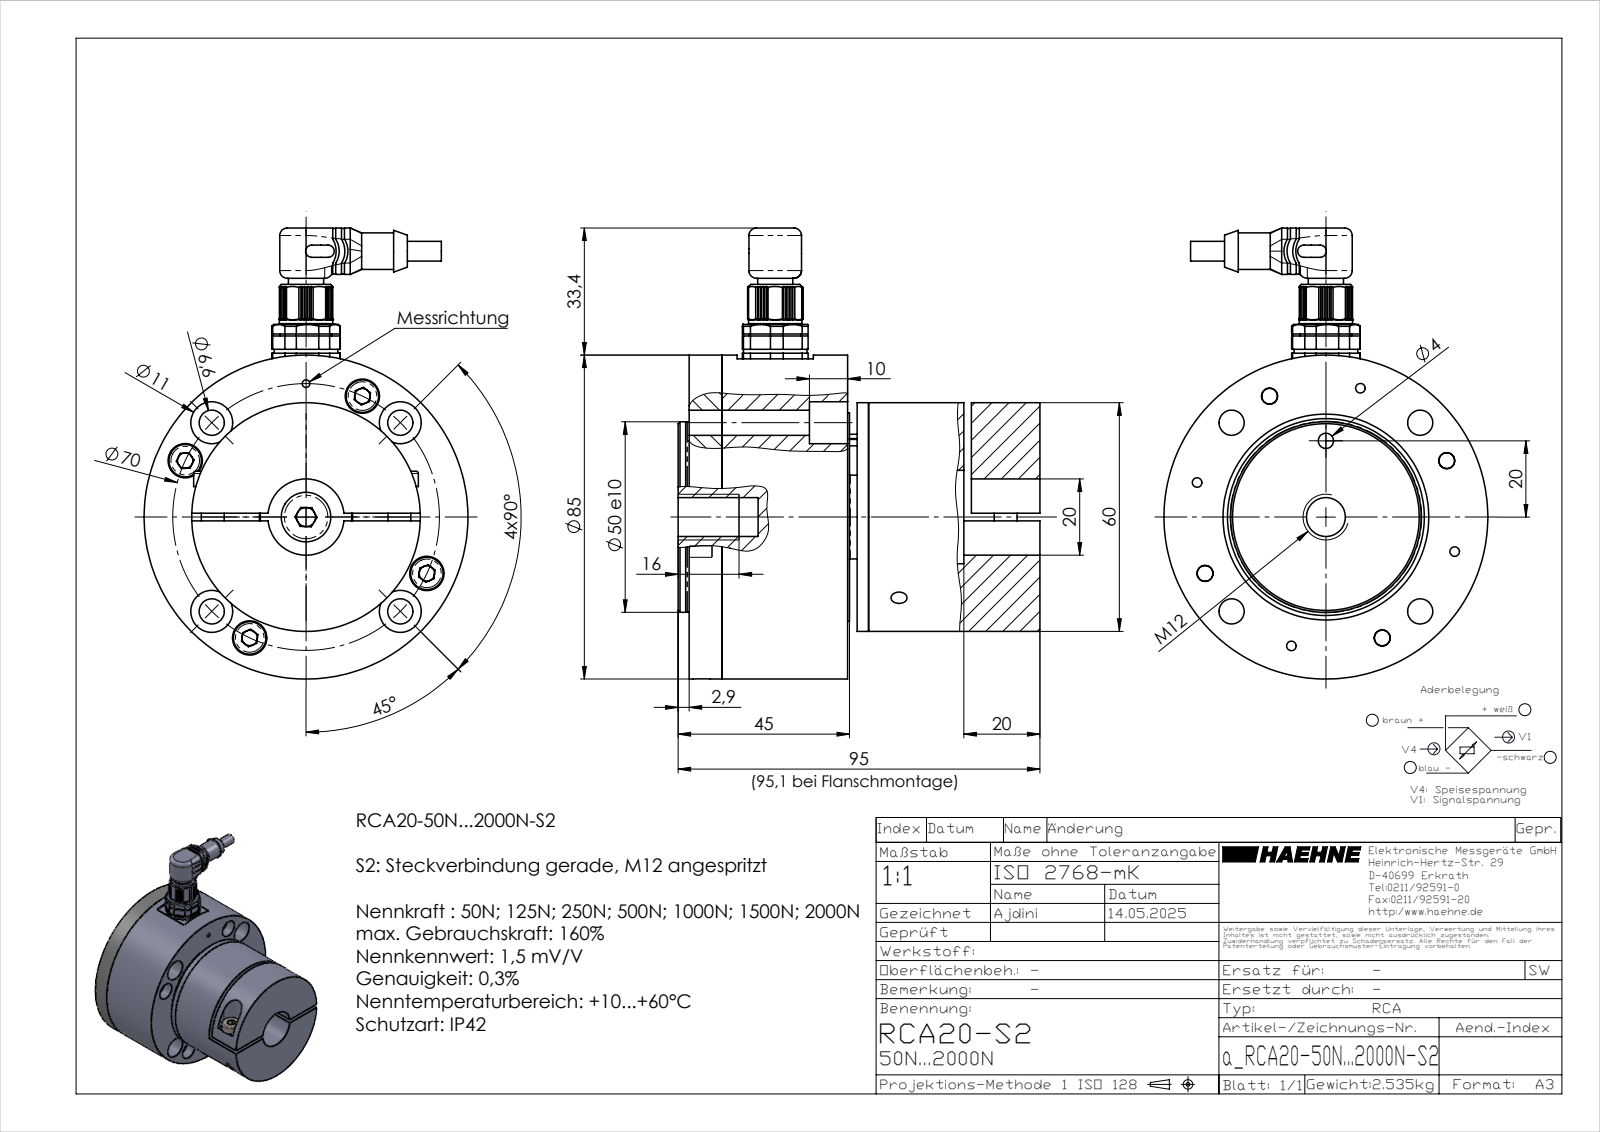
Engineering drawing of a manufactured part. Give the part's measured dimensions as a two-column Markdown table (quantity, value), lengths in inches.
| quantity | value |
| --- | --- |
| part name | inafag_1203-tvh_7zkvytp7yxkimpdvw8sj0b5w4_17; a_RCA20-50N...2000N-S2; RCA20 Oberteil_30; inafag_1203-tvh_7zkvytp7yxkimpdvw8sj0b5w4_25 (+8 more) |
| STEP written by | SolidWorks 2023 (AUTOMOTIVE_DESIGN) |
| units | inches |
| bodies | 53 solids, 1227 faces (663 planar, 295 cylindrical, 269 other) |
| overall size | 4.659 × 3.744 × 3.346 |
| volume | 22.52 in³ |
| surface area | 175 in² |
| round holes (diameter × count) | 0.134 × 9, 0.098 × 8, 0.26 × 6, 0.165 × 5, 0.433 × 5, 0.043 × 4, 0.045 × 4, 0.063 × 4, 0.073 × 4, 0.157 × 4, 0.209 × 4, 0.354 × 4 |
| round bosses / shafts (diameter × count) | 0.118 × 9, 0.224 × 8, 0.335 × 4, 0.197 × 4, 0.071 × 4, 0.061 × 4, 0.059 × 4, 0.039 × 4 |
| partial cylindrical surfaces (radius × count) | 0.008 × 16, 0.012 × 9, 0.016 × 4, 0.021 × 4, 0.039 × 4, 0.05 × 4, 0.236 × 4, 0.063 × 2 |
| main face-to-face distances | 0.118, 0.079, 0.339, 1.854, 1.772, 0.457, 1.181, 1.969, 1.398, 1.972 |
| hole center spacings | 1.378, 1.949, 0.976, 0.992, 1.291, 2.013, 2.223, 0.098 |
